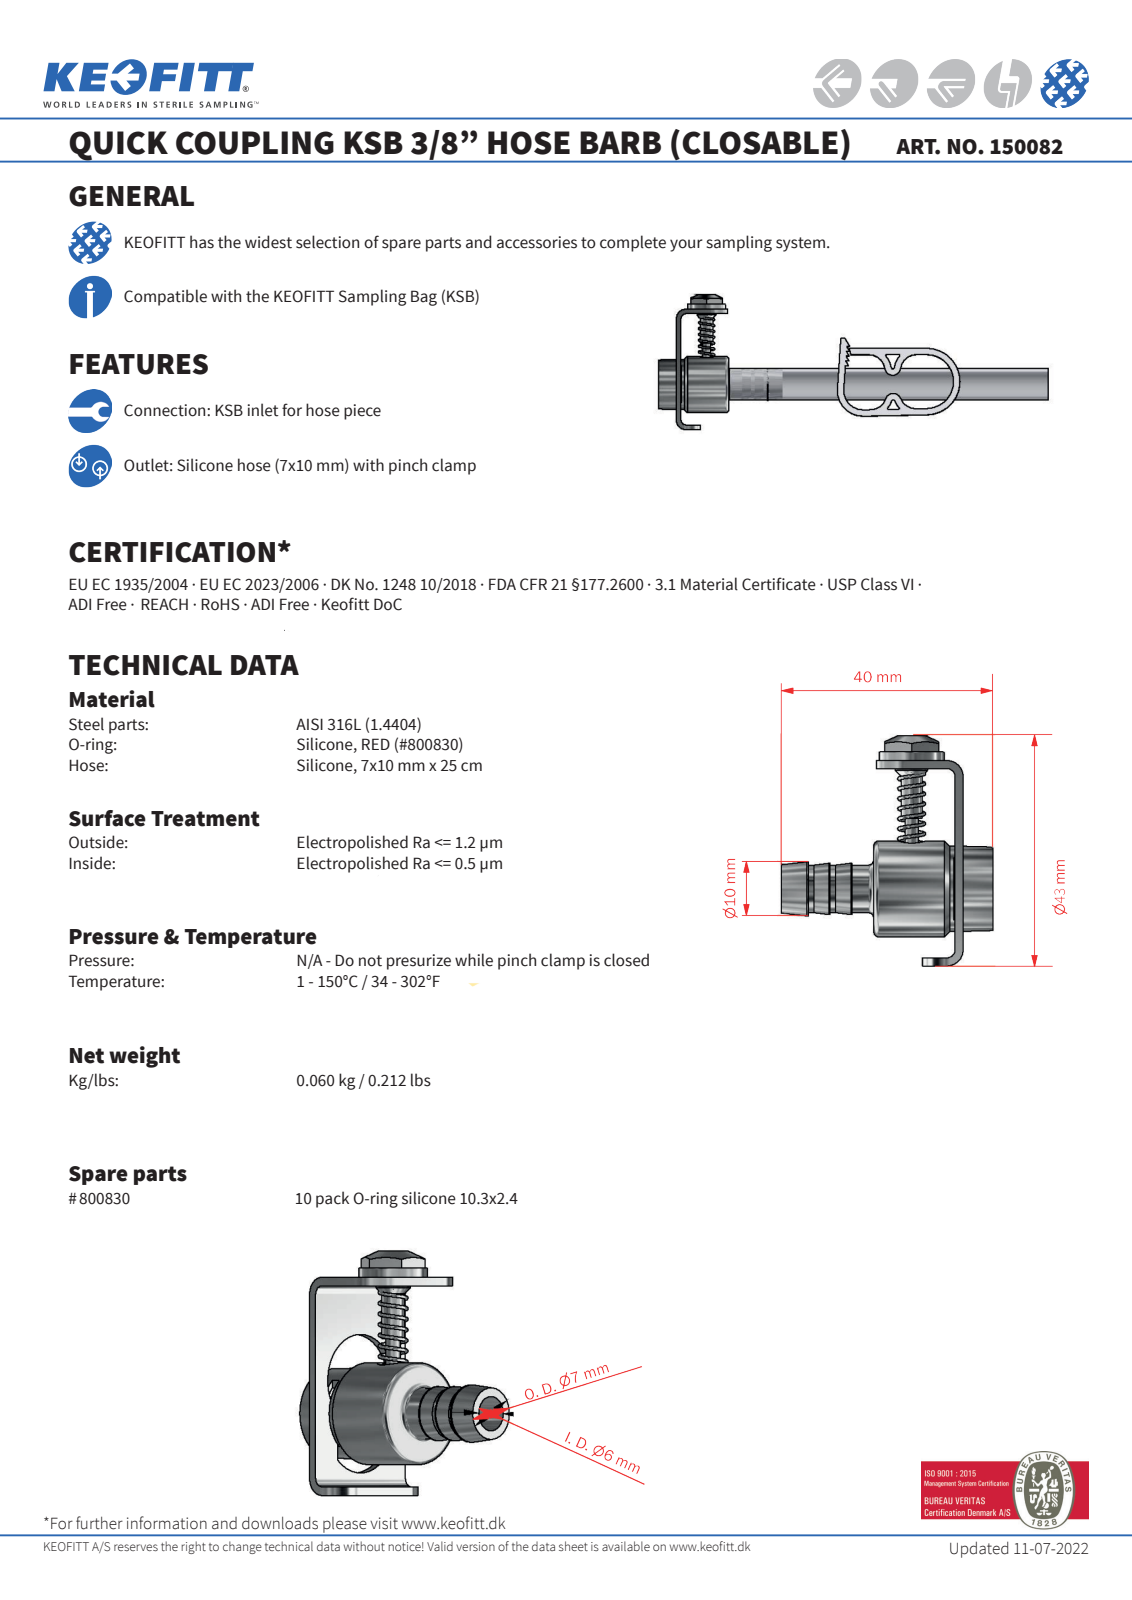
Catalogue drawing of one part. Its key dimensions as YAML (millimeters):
part_name: "150082"
step_written_by: "Autodesk Inventor 2022 (AUTOMOTIVE_DESIGN)"
units: millimeters
bodies: {solids: 1, faces: 98, planar: 56, cylindrical: 34, other: 8}
overall_size: [122.11, 42.6, 22]
volume: 18470
surface_area: 11274
round_holes:
  - {diameter: 14, count: 1}
round_bosses_or_shafts:
  - {diameter: 17.8, count: 1}
  - {diameter: 15.8, count: 1}
  - {diameter: 12, count: 1}
  - {diameter: 10, count: 1}
  - {diameter: 6, count: 1}
  - {diameter: 3.9, count: 1}
  - {diameter: 2.5, count: 1}
partial_cylinders:
  - {radius: 5, count: 9}
  - {radius: 1.5, count: 2}
  - {radius: 2.5, count: 2}
  - {radius: 3, count: 2}
  - {radius: 6, count: 2}
  - {radius: 1.2, count: 1}
  - {radius: 8, count: 1}
  - {radius: 8.5, count: 1}
face_to_face_distances: [1.5, 2, 17, 36.5, 22, 16.5, 15, 1.73, 35, 38]
